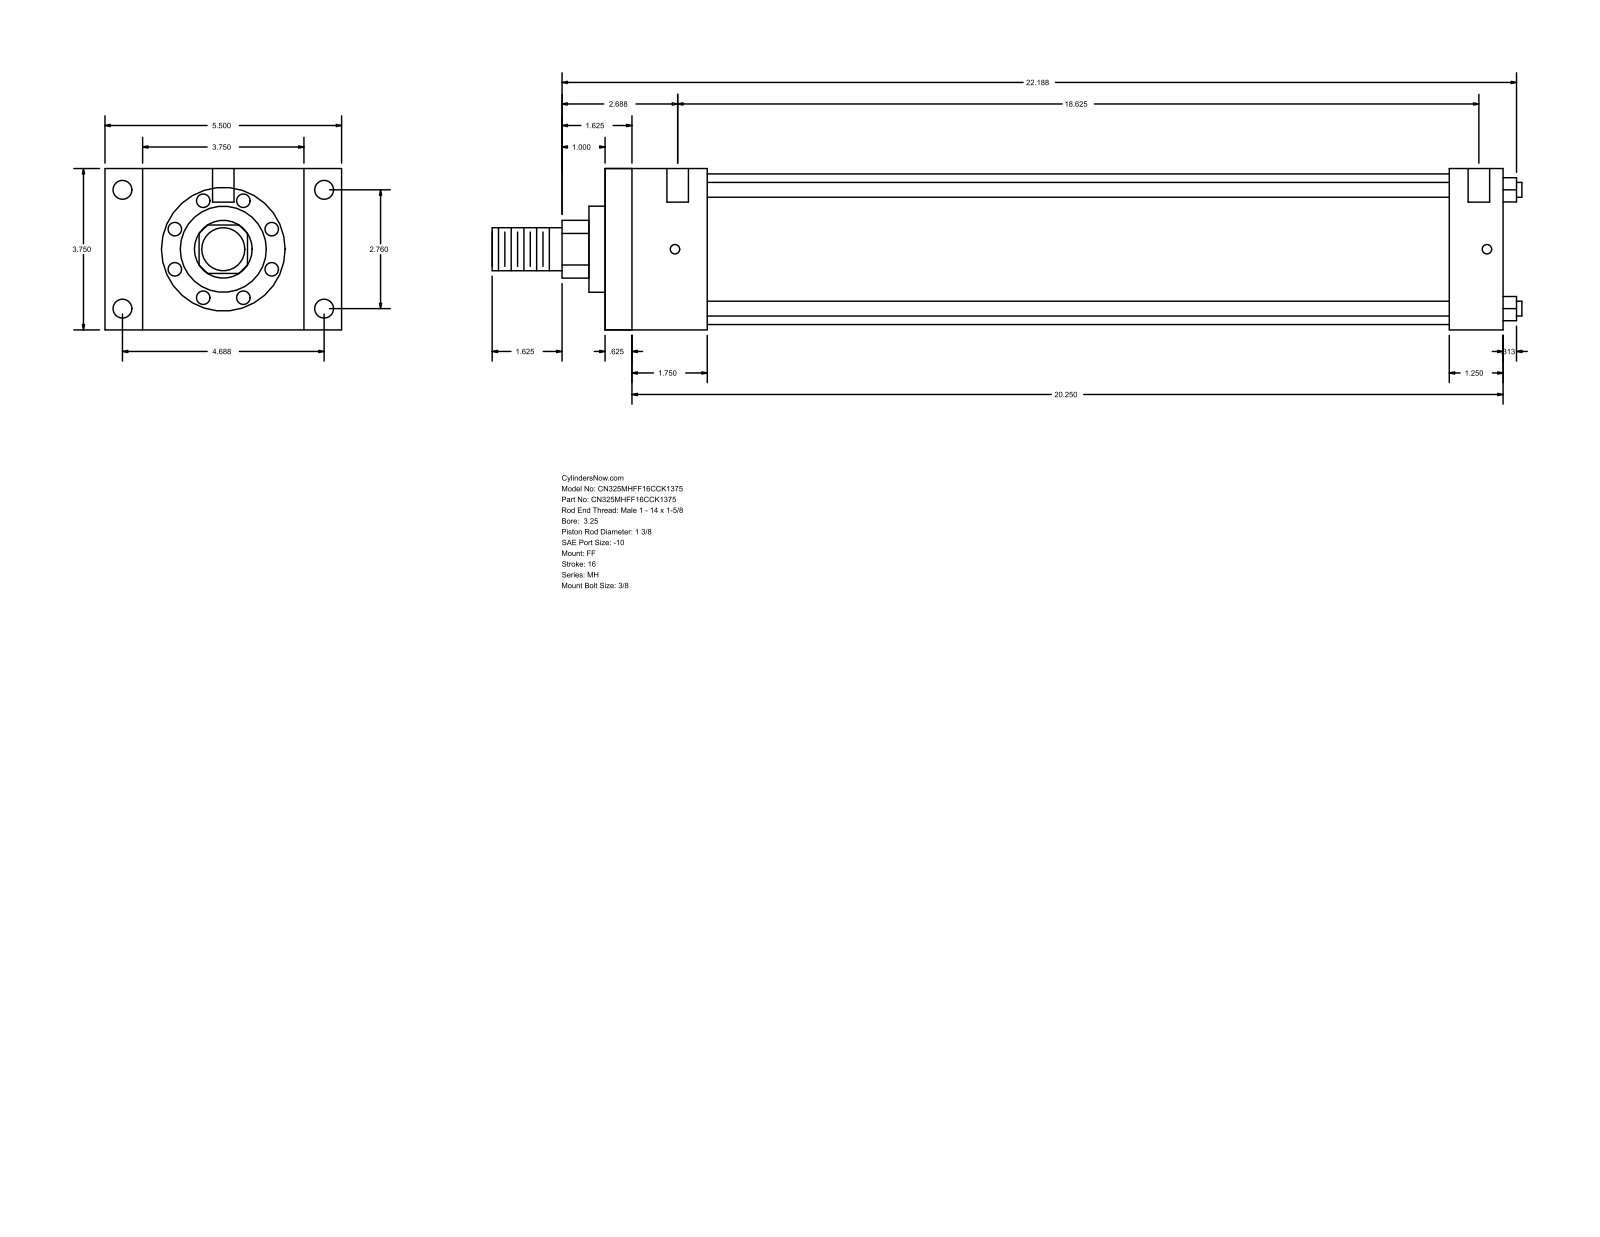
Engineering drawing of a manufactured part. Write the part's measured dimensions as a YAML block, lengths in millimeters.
part_name: "MH_FF__0325_1.375"
step_written_by: "GSSL Pune (CONFIG_CONTROL_DESIGN)"
units: millimeters
bodies: {solids: 0, faces: 92, planar: 64, cylindrical: 28, other: 0}
overall_size: [608.01, 139.7, 95.25]
round_holes:
  - {diameter: 5.56, count: 4}
  - {diameter: 11.13, count: 4}
  - {diameter: 12.7, count: 2}
round_bosses_or_shafts:
  - {diameter: 8.76, count: 4}
  - {diameter: 88.9, count: 1}
  - {diameter: 50.8, count: 1}
  - {diameter: 34.92, count: 1}
  - {diameter: 25.4, count: 1}
partial_cylinders:
  - {radius: 17.06, count: 1}
face_to_face_distances: [95.24, 530.22, 15.87, 514.35, 22.23, 117.47, 498.48, 482.61, 31.74, 60.32]
hole_center_spacings: [70.1, 119.06, 138.16, 479.43, 1.59, 4.76, 473.08, 474.67]
